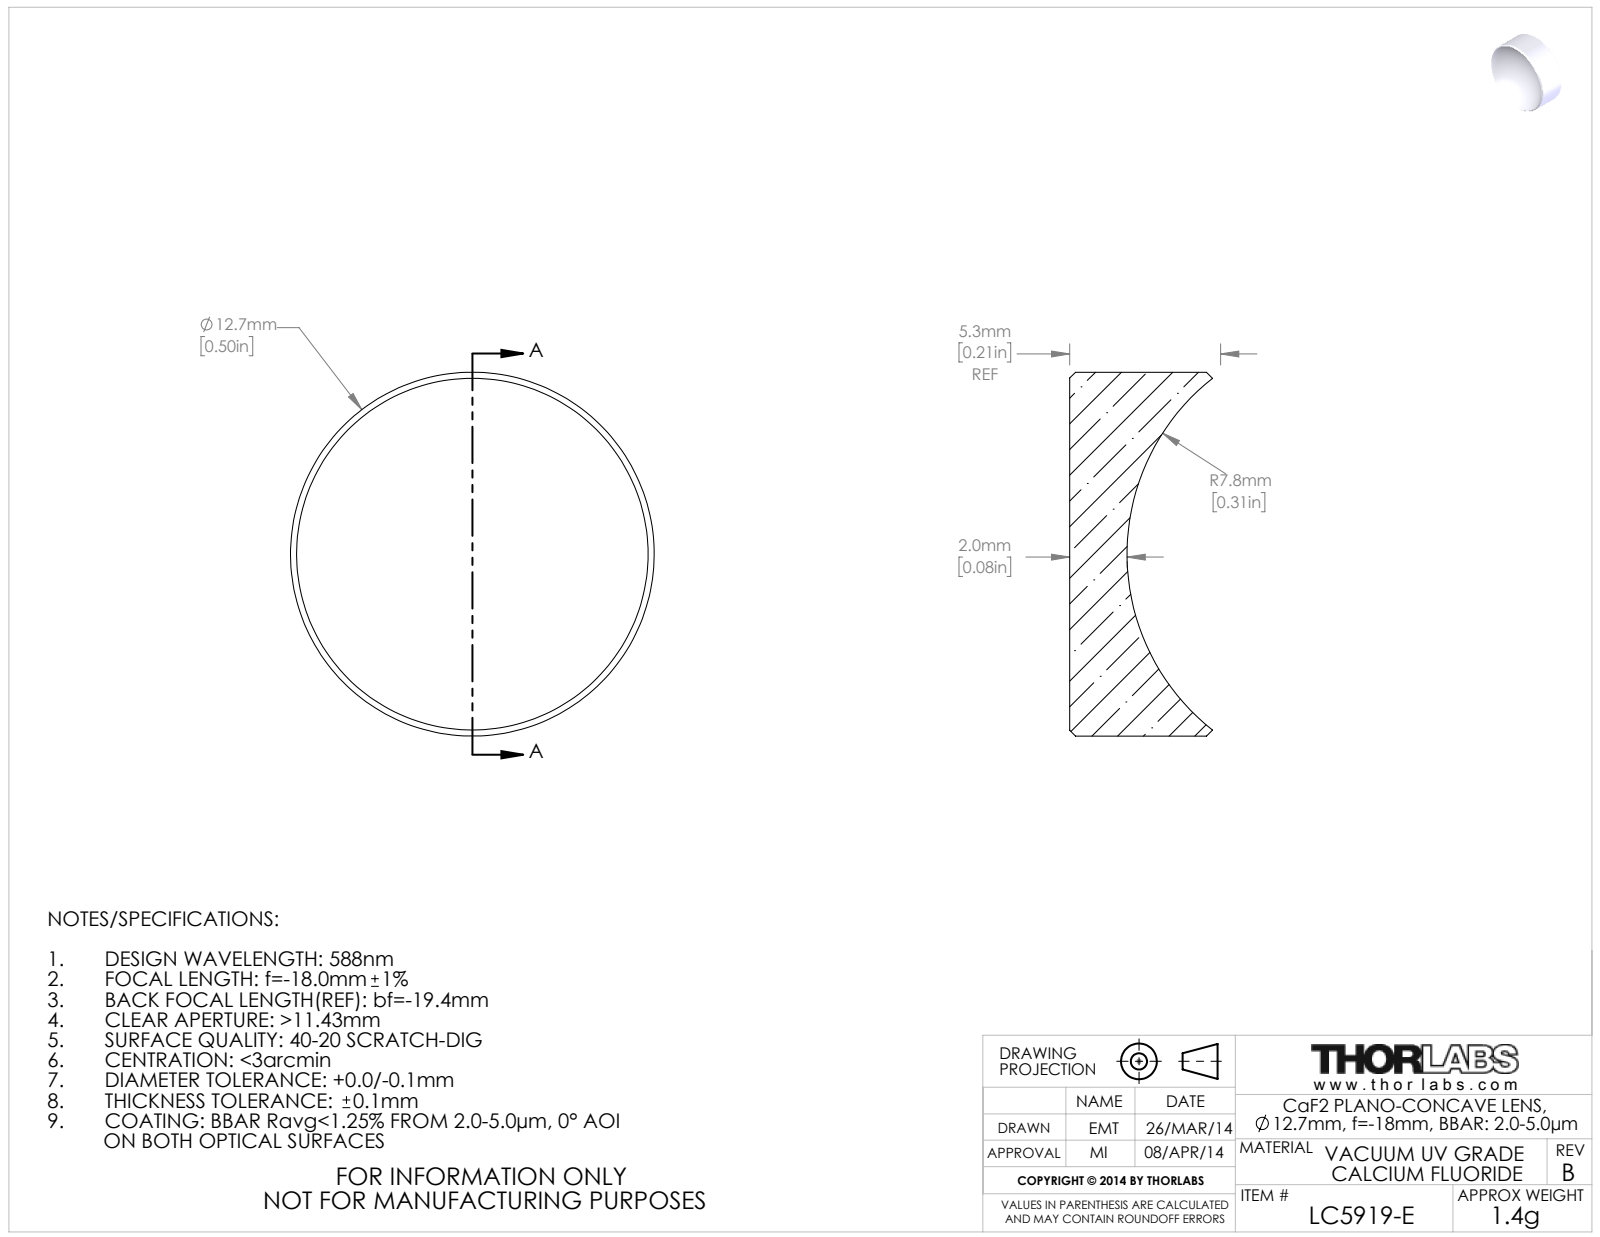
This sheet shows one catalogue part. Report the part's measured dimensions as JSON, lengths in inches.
{"part_name": "20141-E0W", "step_written_by": "SolidWorks 2016 (CONFIG_CONTROL_DESIGN)", "units": "inches", "bodies": {"solids": 1, "faces": 9, "planar": 1, "cylindrical": 2, "other": 6}, "overall_size": [0.5, 0.5, 0.196], "volume_in3": 0.027, "surface_area_in2": 0.729, "round_bosses_or_shafts": [[0.5, 1]]}
